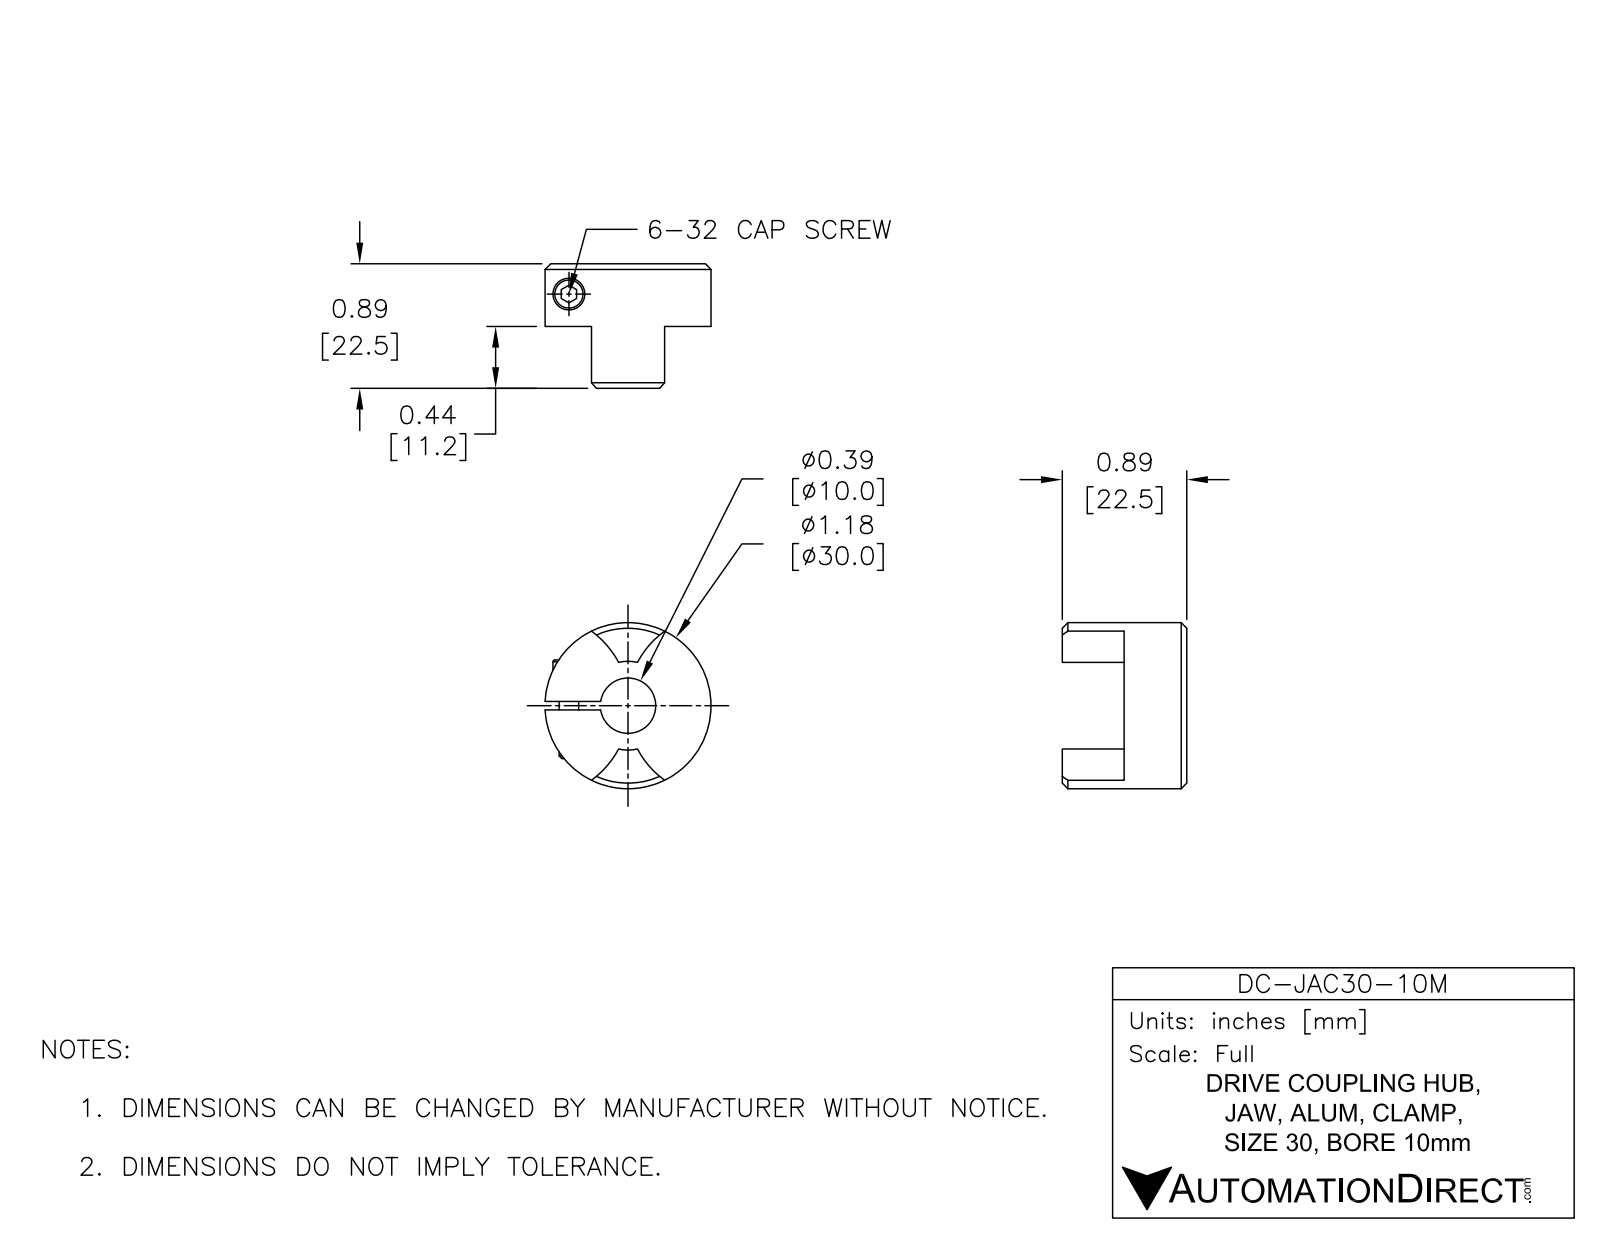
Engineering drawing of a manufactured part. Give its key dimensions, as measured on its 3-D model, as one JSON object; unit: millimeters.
{"part_name": "DC-JAC30-10M", "step_written_by": "SolidWorks 2015 (AUTOMOTIVE_DESIGN)", "units": "millimeters", "bodies": {"solids": 1, "faces": 27, "planar": 7, "cylindrical": 16, "other": 4}, "overall_size": [29.97, 29.95, 22.48], "volume_mm3": 7761, "surface_area_mm2": 3678, "round_holes": [[3.91, 1], [6.35, 1], [10, 1]], "round_bosses_or_shafts": [[29.97, 1]], "partial_cylinders_radius": [[16.64, 2], [8, 1]], "face_to_face_distances": [11.3, 1.52, 22.48, 11.18, 5.51, 3.99]}
